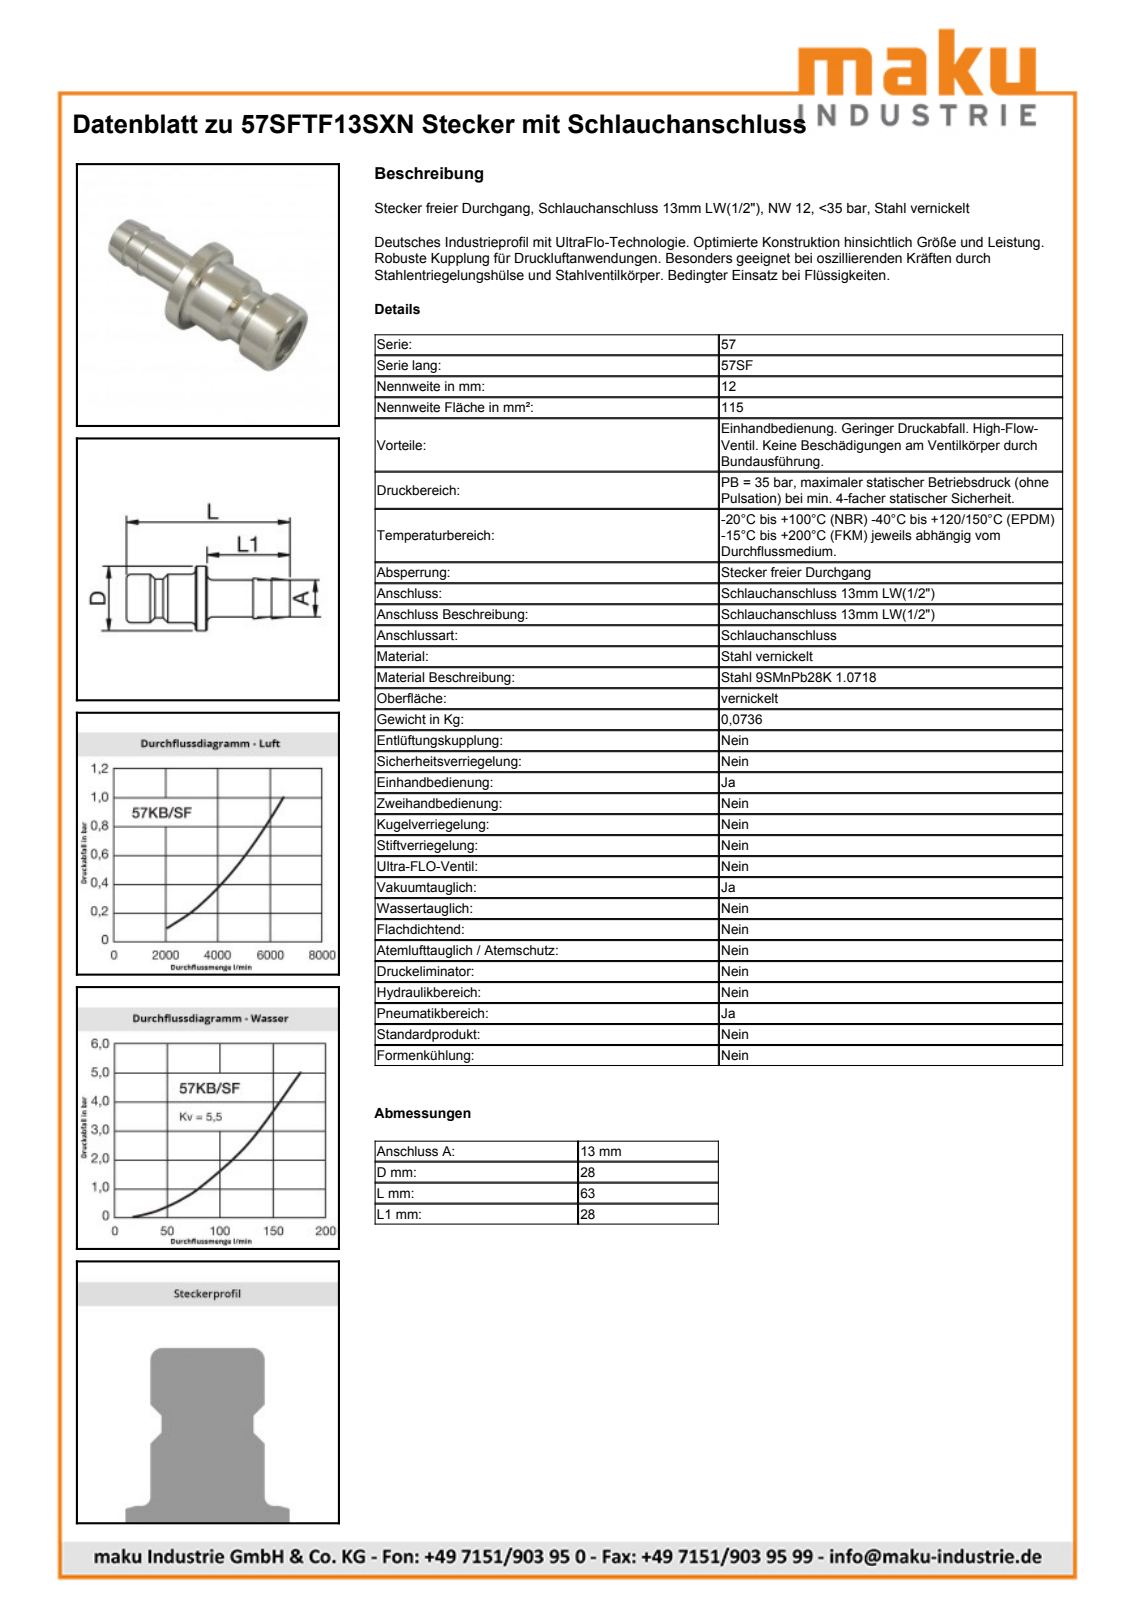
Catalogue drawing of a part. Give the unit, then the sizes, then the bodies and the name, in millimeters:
Units: millimetres
Overall size (bounding box): 63 × 28 × 28
Round holes (diameter × count): ⌀10 ×1, ⌀13.5 ×1
Round bosses / shafts (diameter × count): ⌀28 ×1, ⌀20.9 ×1, ⌀16.8 ×1, ⌀13 ×1
Main face-to-face distances: 5, 30, 35, 6, 63, 33, 28, 57, 27, 22
Volume: 9 504 mm³ · Surface area: 6 813 mm²
Bodies: 1 solid, 26 faces (6 planar, 7 cylindrical, 13 other)
Part name (STEP PRODUCT): D110176
STEP written by: Autodesk Inventor 2013 (AUTOMOTIVE_DESIGN)
